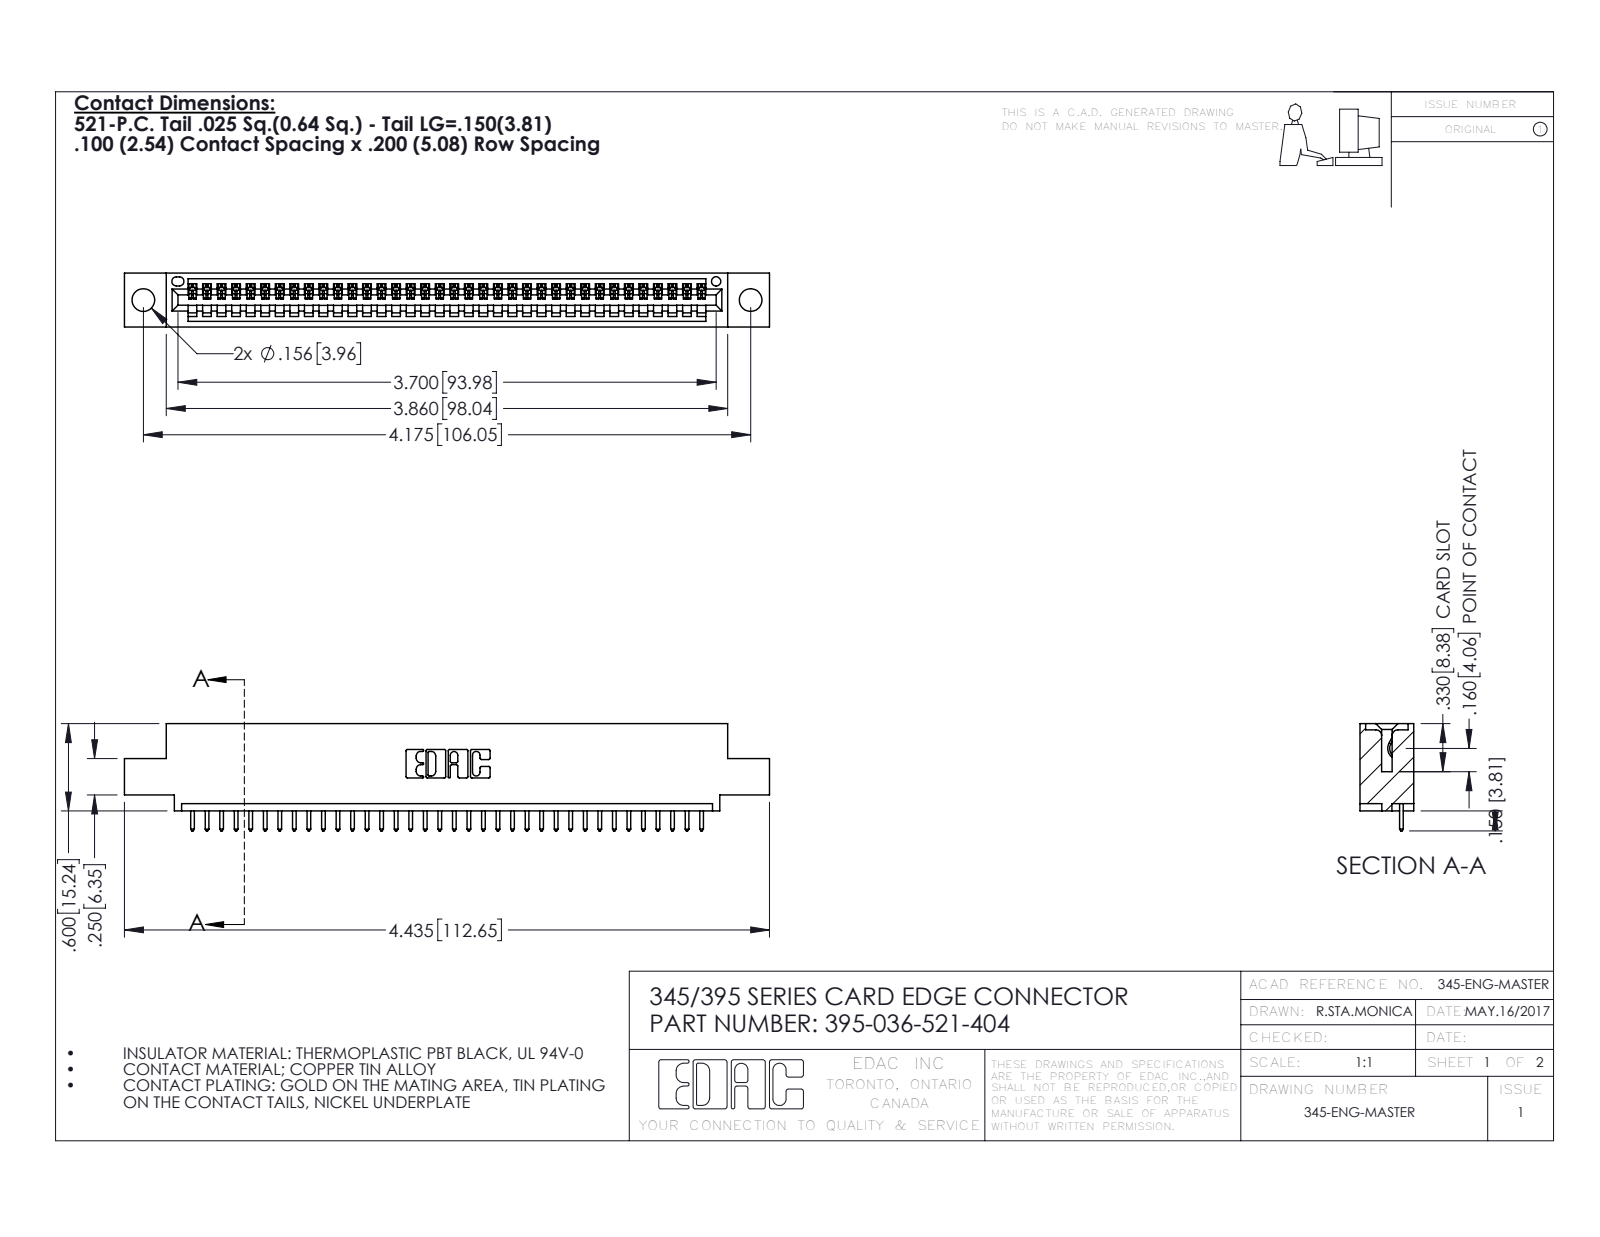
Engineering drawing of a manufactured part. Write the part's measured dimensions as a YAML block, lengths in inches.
part_name: "345 Part_0.110 Offset - 0.156 Dia-TH; 345-292-001_345-293-121; 395-036-521-404"
step_written_by: "SolidWorks 2016 (CONFIG_CONTROL_DESIGN)"
units: inches
bodies: {solids: 37, faces: 2218, planar: 1524, cylindrical: 694, other: 0}
overall_size: [4.435, 0.737, 0.37]
volume: 0.634
surface_area: 20.48
round_holes:
  - {diameter: 0.156, count: 2}
  - {diameter: 0.064, count: 1}
partial_cylinders:
  - {radius: 0.006, count: 72}
  - {radius: 0.01, count: 72}
  - {radius: 0.01, count: 22}
  - {radius: 0.007, count: 6}
  - {radius: 0.031, count: 6}
  - {radius: 0.026, count: 3}
  - {radius: 0.031, count: 2}
  - {radius: 0.04, count: 2}
face_to_face_distances: [0.298, 0.072, 0.37, 0.2, 0.098, 0.272, 0.025, 0.225, 0.149, 0.072]
hole_center_spacings: [0.27, 3.939, 4.175]
